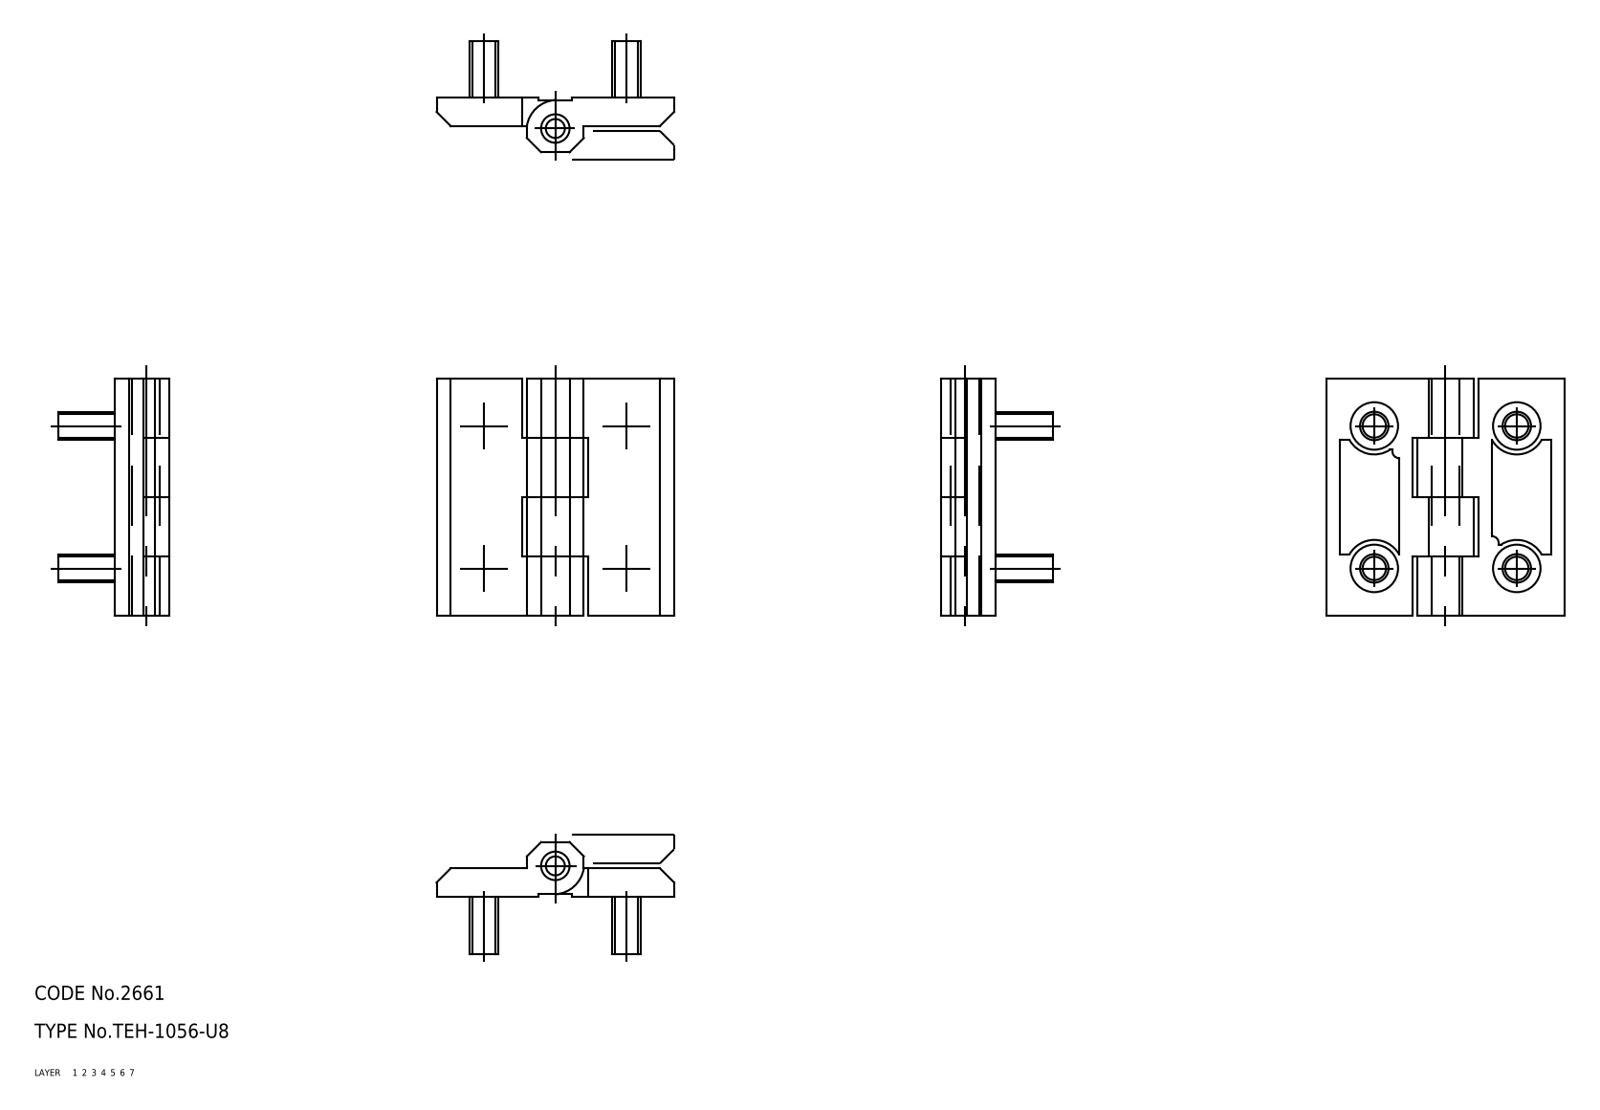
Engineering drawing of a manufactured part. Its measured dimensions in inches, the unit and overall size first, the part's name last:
Units: inches
Overall size (bounding box): 1.969 × 1.969 × 0.925
Volume: 0.962 in³ · Surface area: 17.33 in²
Bodies: 7 solids, 118 faces (0 planar, 0 cylindrical, 118 other)
Part name (STEP PRODUCT): screw; shaft; hinge pieces_B; hinge pieces_A (+1 more)
STEP written by: CADfix (AUTOMOTIVE_DESIGN)
